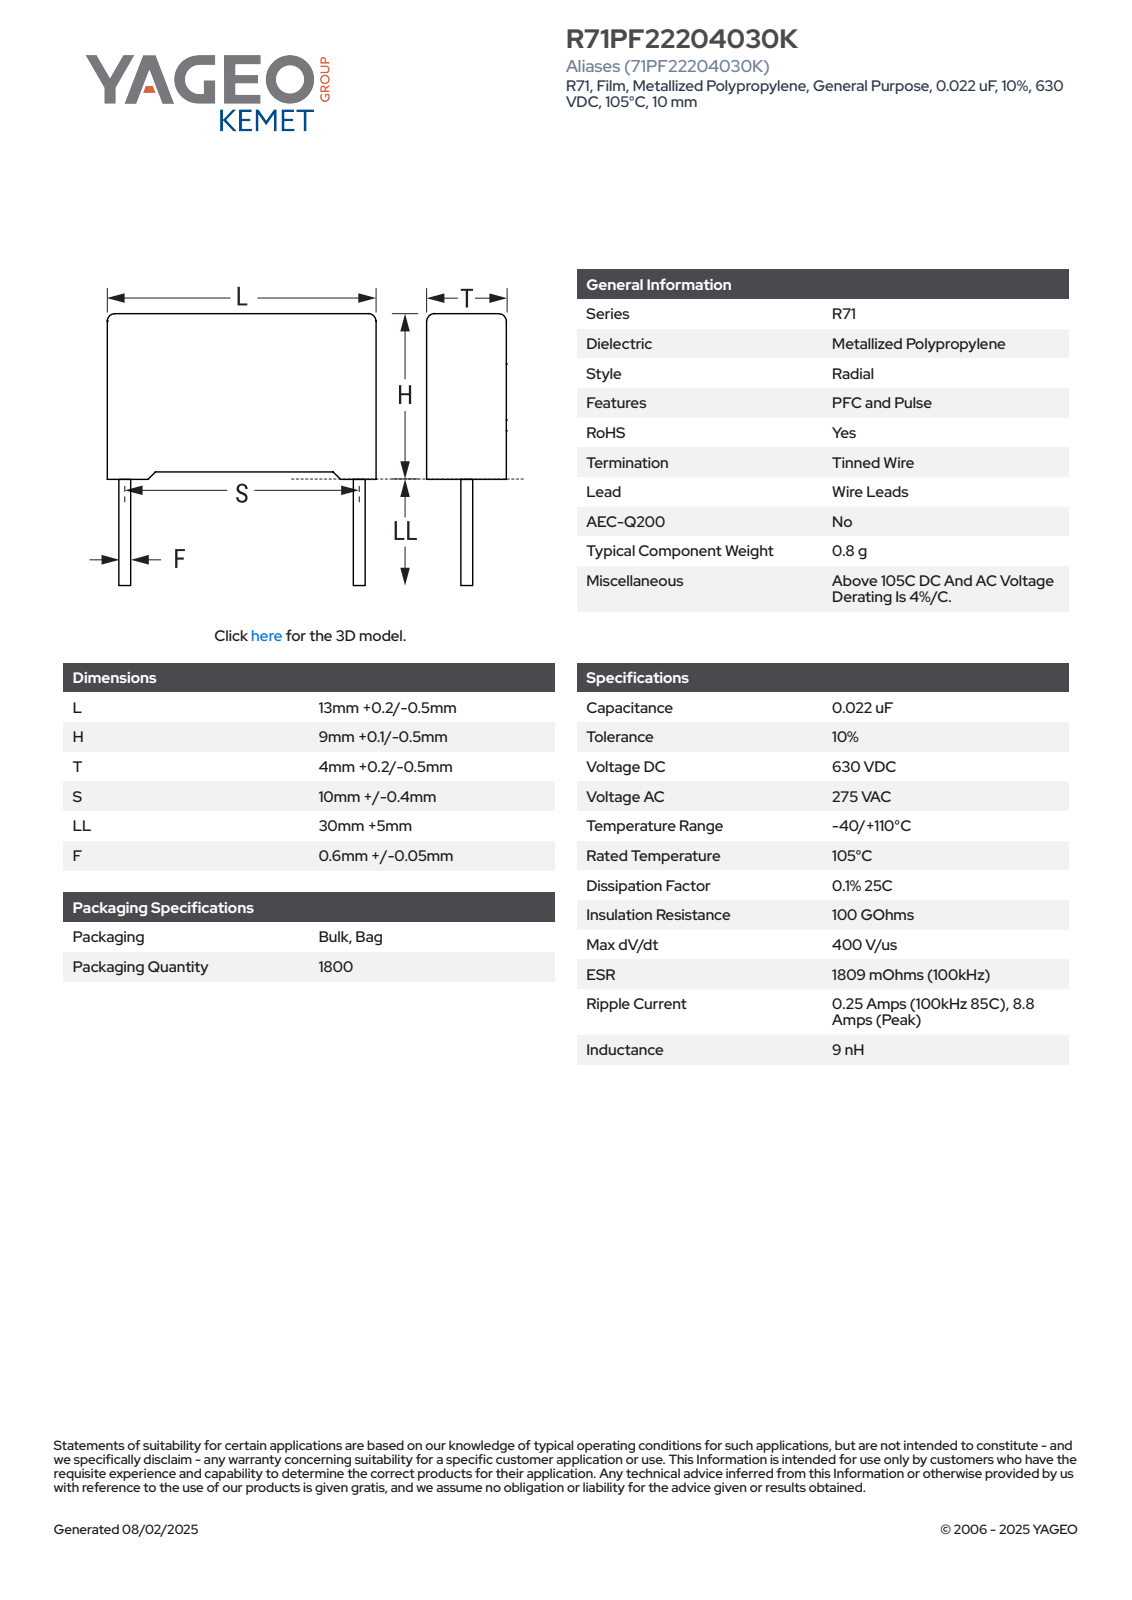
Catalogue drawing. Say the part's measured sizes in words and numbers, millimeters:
The part is named "CFR_RB2_13X9X4_L13.2H9.1T4.2S10LL35F0.65". Its 3-D file was written by "SolidWorks 2021 (AUTOMOTIVE_DESIGN)". It is 4 solids with 85 faces: 77 planar, 8 cylindrical and 0 other. Overall it measures 44.1 by 13.2 by 4.21 millimeters. Its volume is 494 cubic millimeters and its surface area 594 square millimeters. Round bosses or shafts: 2 of diameter 0.65. Partial cylindrical surfaces (rounded edges, fillets, slot ends): 4 of radius 0.5. The main face-to-face distances are 4.2, 8.35, 13.2, 0.44, 3.76, 0.75, 9.1, 3.32, 0.31, 8.79.
